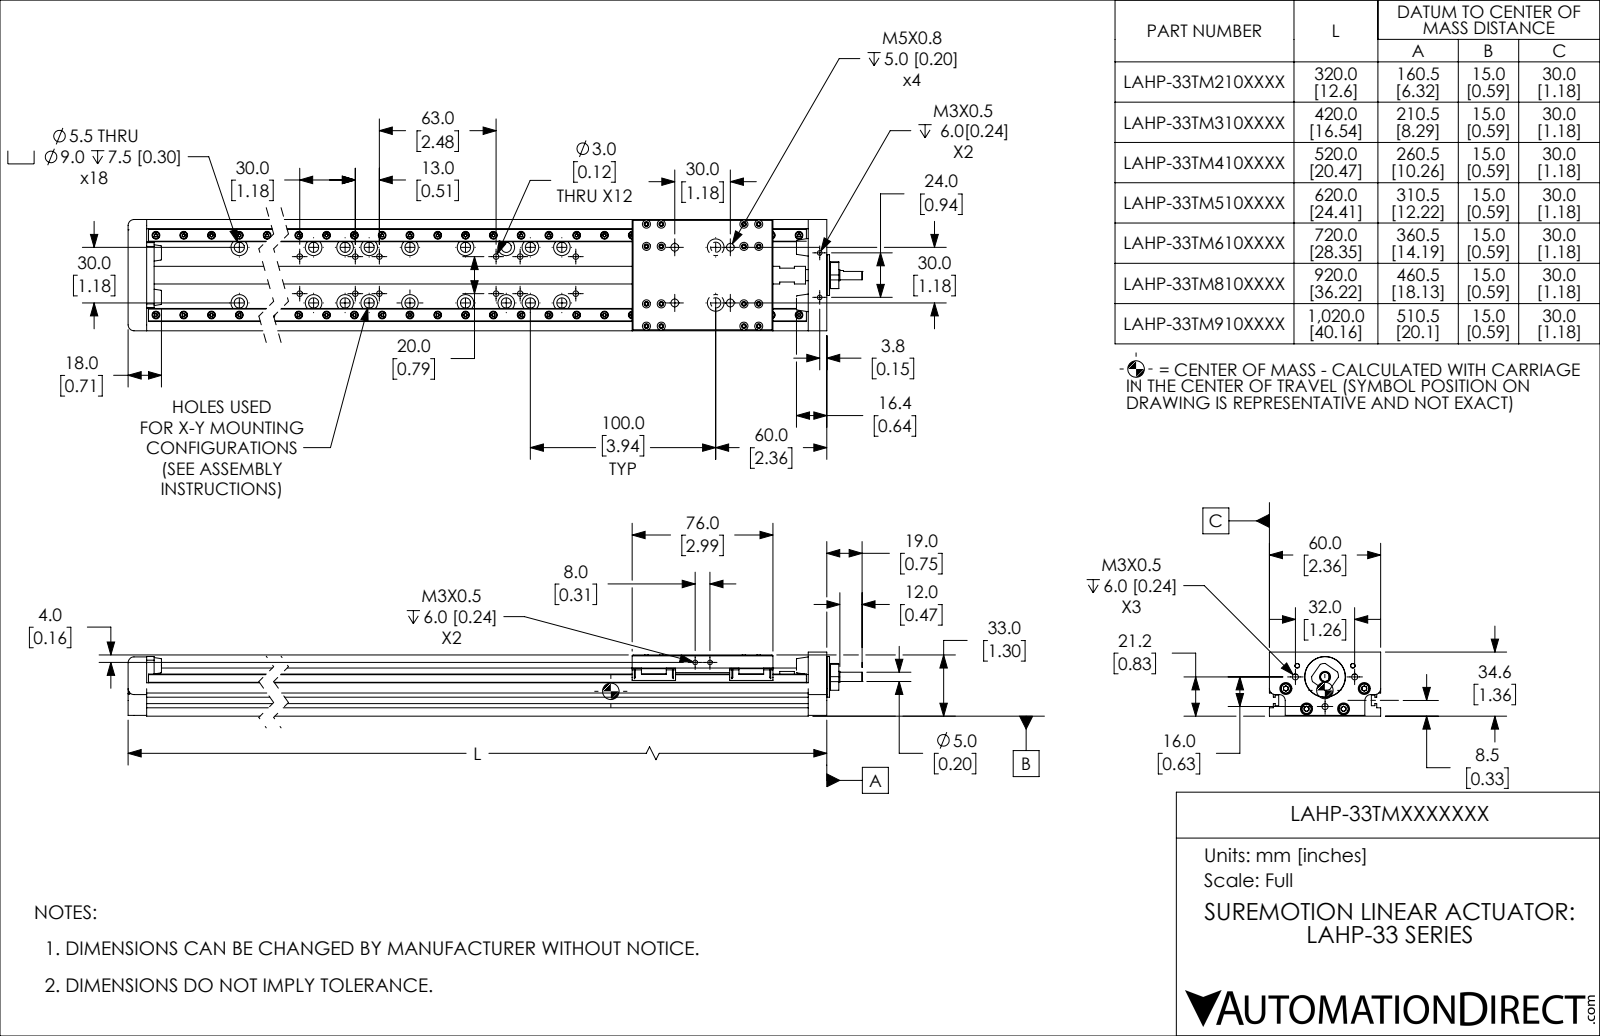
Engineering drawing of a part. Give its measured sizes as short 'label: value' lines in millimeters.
name: LAHP-33TM510B10M; LAHP-33TM510B10M_CARRIAGE; LAHP-33TM510B10M_BASE
written by: SolidWorks 2019 (CONFIG_CONTROL_DESIGN)
unit: mm
bodies: 2 solids, 4459 faces (2068 planar, 1329 cylindrical, 1062 other)
size: 639.1 × 60 × 34.6
volume: 564 900 mm³; area: 206 800 mm²
holes: 84× ⌀4.2, 82× ⌀1.6, 80× ⌀2.4, 24× ⌀5.5, 24× ⌀9, 16× ⌀1.6, 16× ⌀2.6, 16× ⌀4.4, 14× ⌀2.5, 14× ⌀3, 7× ⌀3.6, 7× ⌀6.5
bosses: 80× ⌀3.8, 80× ⌀2, 11× ⌀5.5, 11× ⌀3, 2× ⌀5.7, 1× ⌀22, 1× ⌀19, 1× ⌀14.5
rounds: 15× R3.2, 8× R0.2, 8× R0.5, 4× R0.9, 2× R0.3, 1× R7.3
face distances: 7.8, 12, 48, 7, 43, 5, 55, 22.7, 14.9, 60
hole spacings: 30, 100, 104.4, 35, 52, 60, 200, 202.2
